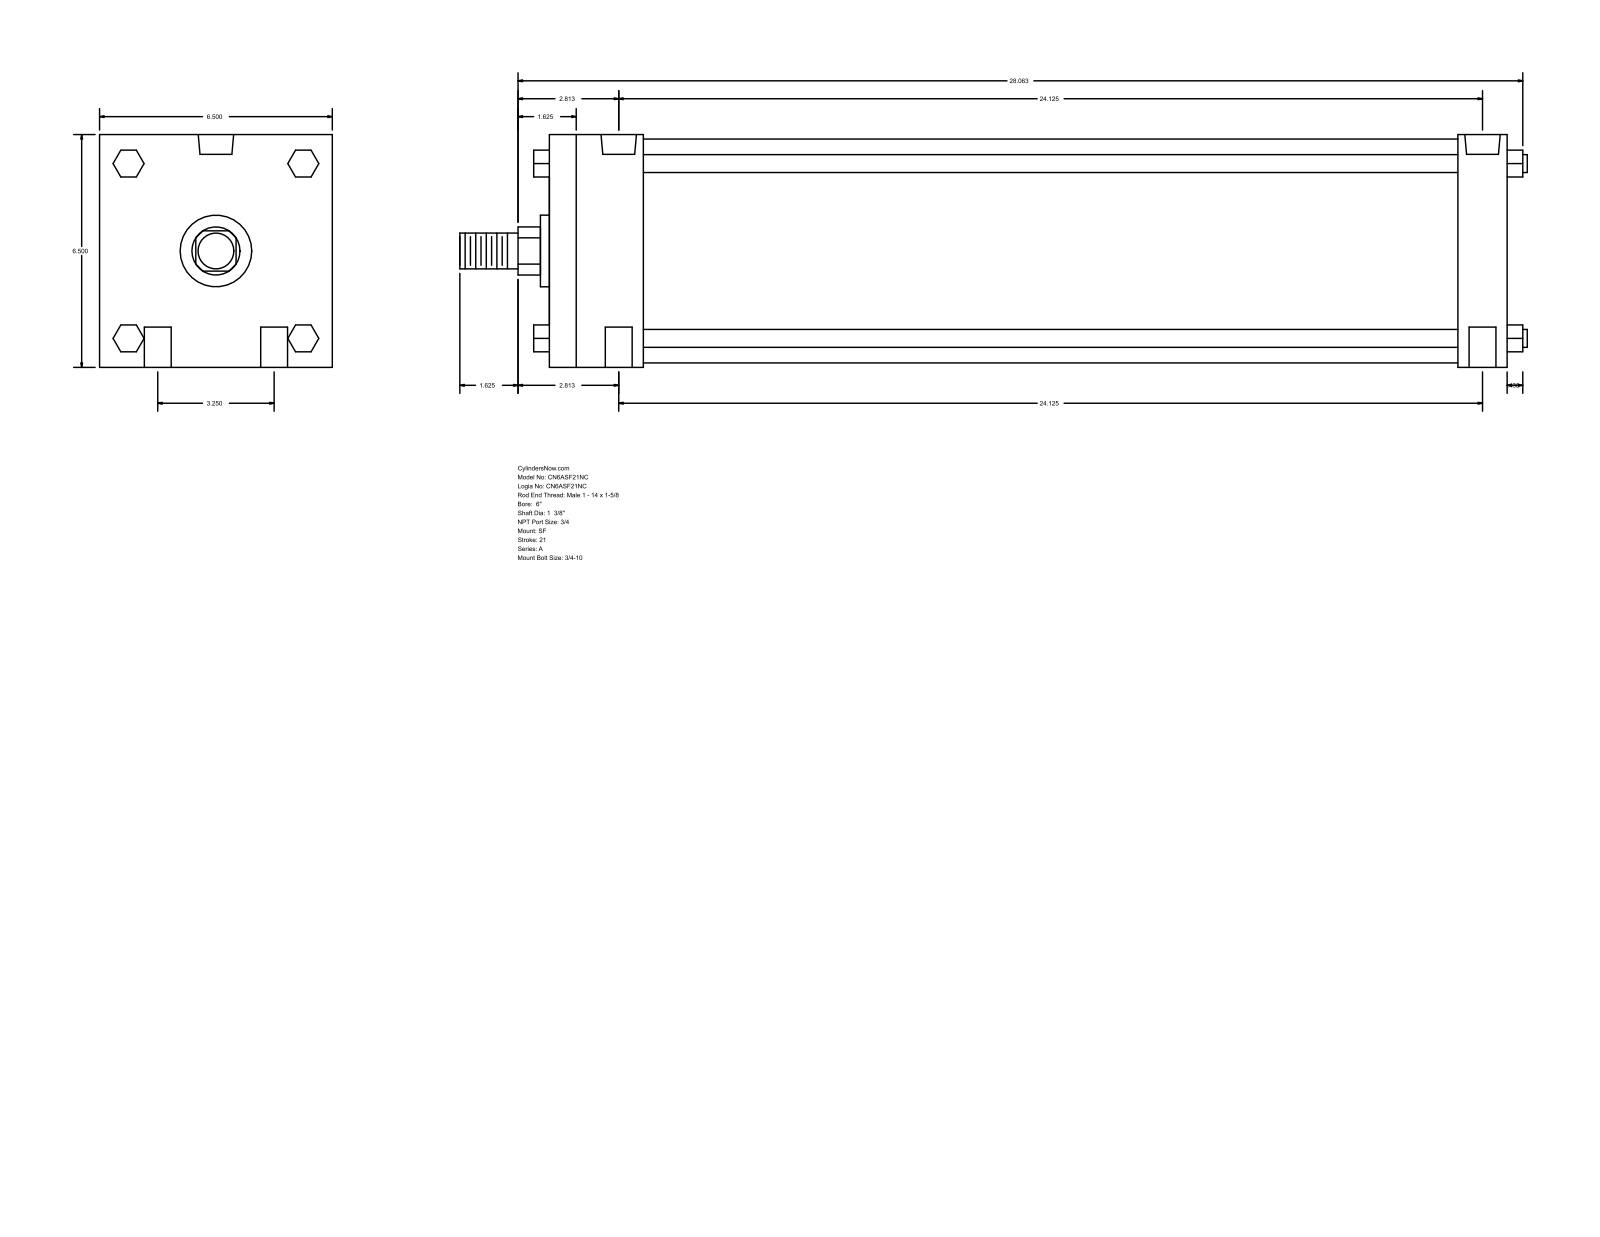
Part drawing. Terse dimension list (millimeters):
name: A_SF__0600_1.375
written by: GSSL Pune (CONFIG_CONTROL_DESIGN)
unit: mm
bodies: 0 solids, 124 faces (94 planar, 30 cylindrical, 0 other)
size: 757.24 × 165.1 × 165.1
holes: 4× ⌀19.05, 2× ⌀15.08, 2× ⌀25.12
bosses: 4× ⌀12.7, 1× ⌀158.75, 1× ⌀50.8, 1× ⌀34.92, 1× ⌀25.4
rounds: 1× R17.06
face distances: 165.1, 679.44, 644.52, 34.92, 66.67, 577.85, 612.77, 19.05, 61.97, 107.34
hole spacings: 41.27, 614.16, 612.77, 82.54, 618.3, 601.65
